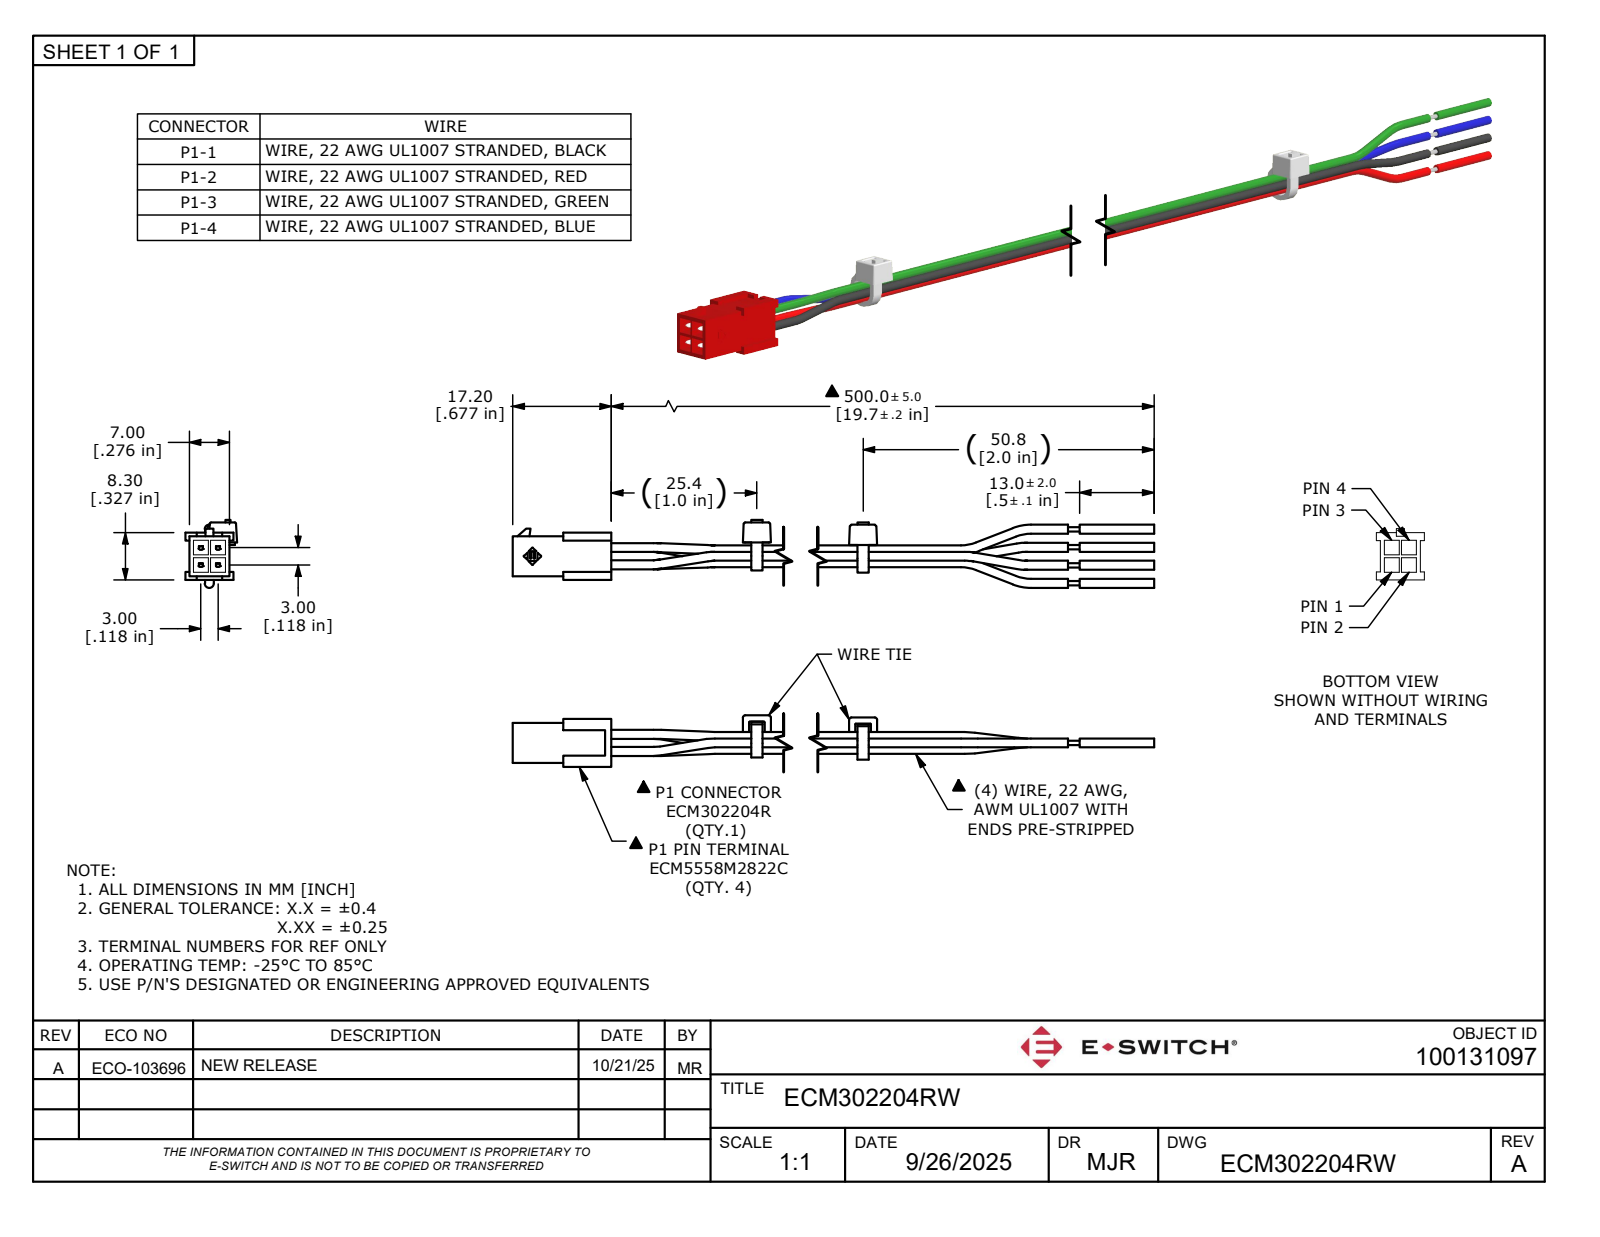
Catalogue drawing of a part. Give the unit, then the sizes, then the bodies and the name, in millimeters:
Units: millimetres
Overall size (bounding box): 517.2 × 11.8 × 9
Round bosses / shafts (diameter × count): ⌀1.6 ×20, ⌀0.8 ×4
Partial cylindrical surfaces — rounded edges, fillets, slot ends (radius × count): R0.2 ×38, R0.2 ×22, R0.3 ×20, R0.2 ×18, R0.4 ×16, R0.6 ×16, R0.5 ×6, R1.6 ×6
Main face-to-face distances: 0.7, 6.3, 3, 7, 3.3, 3.8, 3.3, 2.5, 3, 5.6
Volume: 4 620 mm³ · Surface area: 12 140 mm²
Bodies: 5 solids, 1069 faces (557 planar, 308 cylindrical, 204 other)
Part name (STEP PRODUCT): ECM302204RW
STEP written by: Autodesk Inventor 2022 (AUTOMOTIVE_DESIGN)
